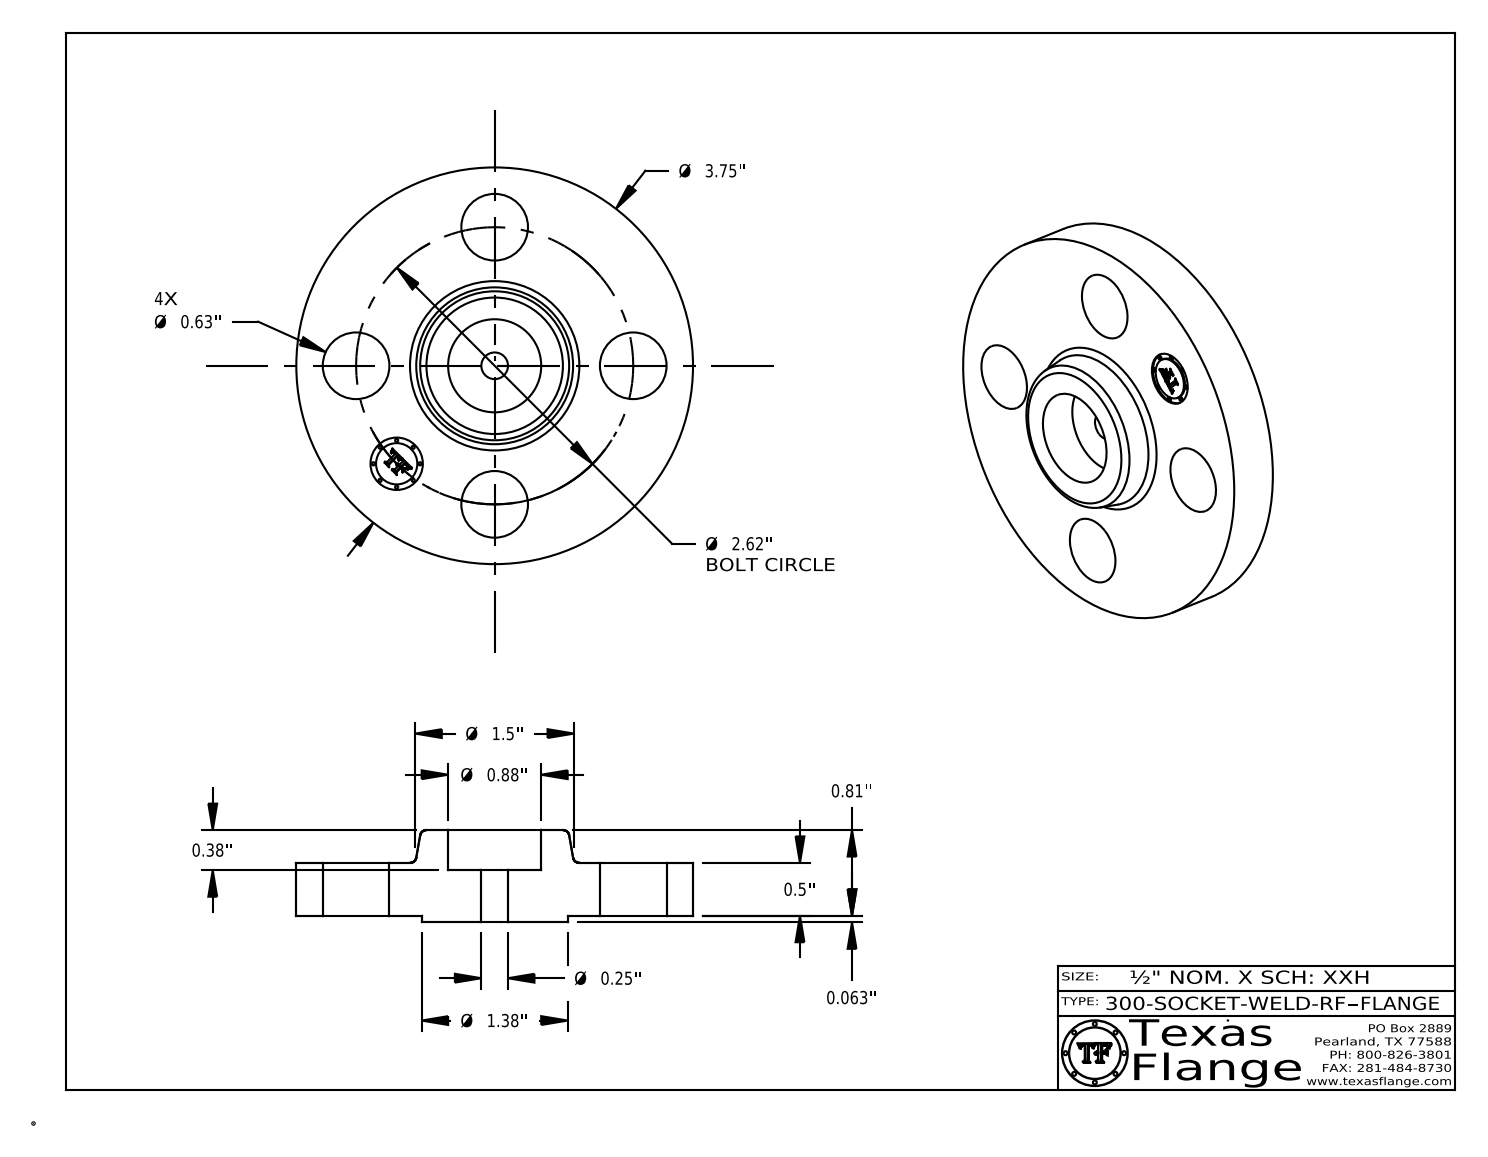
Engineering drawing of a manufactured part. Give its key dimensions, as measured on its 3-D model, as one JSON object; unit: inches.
{"part_name": "300-SOCKET-WELD-RF", "step_written_by": "CATIA V5 STEP AP214 (AUTOMOTIVE_DESIGN)", "units": "inches", "bodies": {"solids": 1, "faces": 412, "planar": 370, "cylindrical": 36, "other": 6}, "overall_size": [3.75, 3.75, 0.873], "volume_in3": 5.245, "surface_area_in2": 32.18, "round_holes": [[0.63, 4], [0.252, 1], [0.495, 1], [0.88, 1]], "round_bosses_or_shafts": [[0.03, 8], [3.75, 1], [1.38, 1], [0.39, 1]], "face_to_face_distances": [0.5, 0.063, 0.563, 0.872, 0.81, 0.31, 0.07, 0.493, 0.43, 0.38], "hole_center_spacings": [1.31, 1.852, 1.003, 2.42, 2.62, 1.31]}
